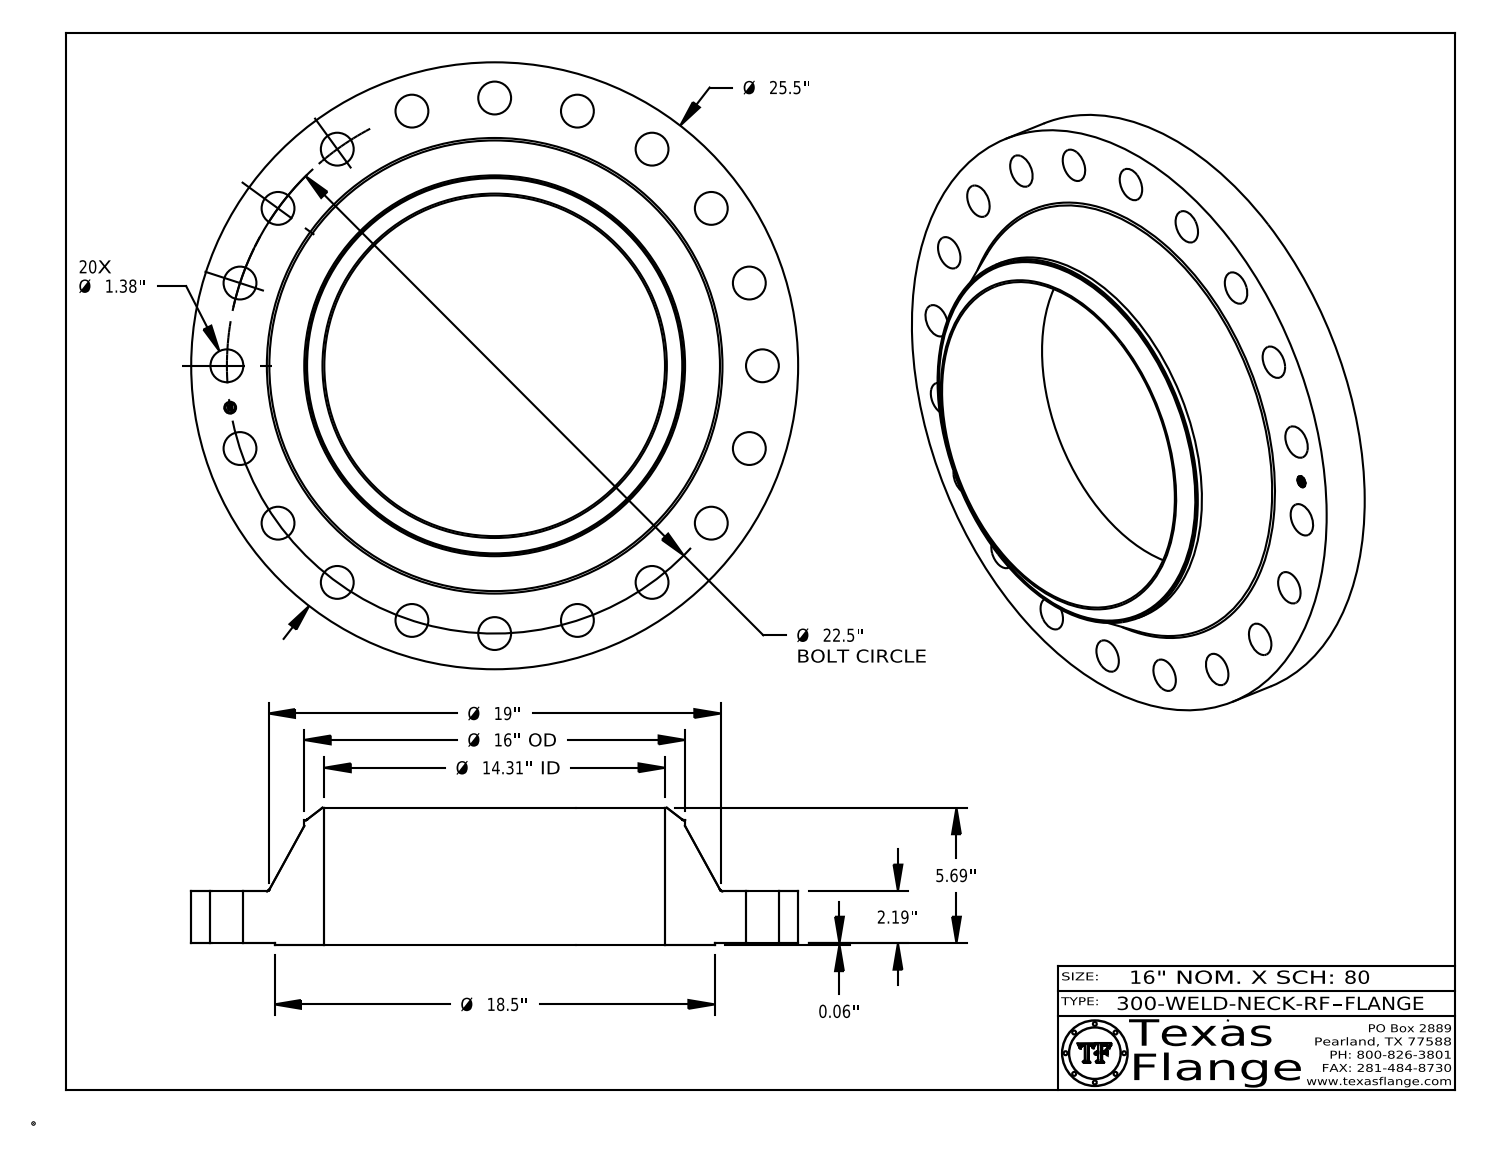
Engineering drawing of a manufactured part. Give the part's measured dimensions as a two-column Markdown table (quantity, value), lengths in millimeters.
| quantity | value |
| --- | --- |
| part name | 300-WELD-NECK-RF |
| STEP written by | CATIA V5 STEP AP214 (AUTOMOTIVE_DESIGN) |
| units | millimeters |
| bodies | 1 solid, 447 faces (369 planar, 68 cylindrical, 10 other) |
| overall size | 647.7 × 647.7 × 146.1 |
| volume | 15 510 000 mm³ |
| surface area | 887 700 mm² |
| round holes (diameter × count) | 35.1 × 20, 12.6 × 1, 363.5 × 1 |
| round bosses / shafts (diameter × count) | 0.8 × 8, 647.7 × 1, 469.9 × 1, 406.4 × 1, 9.9 × 1 |
| main face-to-face distances | 55.6, 1.6, 57.2, 146.1, 144.5, 88.9, 56.8, 55.2, 0.4, 89.3 |
| hole center spacings | 285.8, 176.6, 335.9, 89.4, 462.4, 509.2, 543.5, 564.5 |
